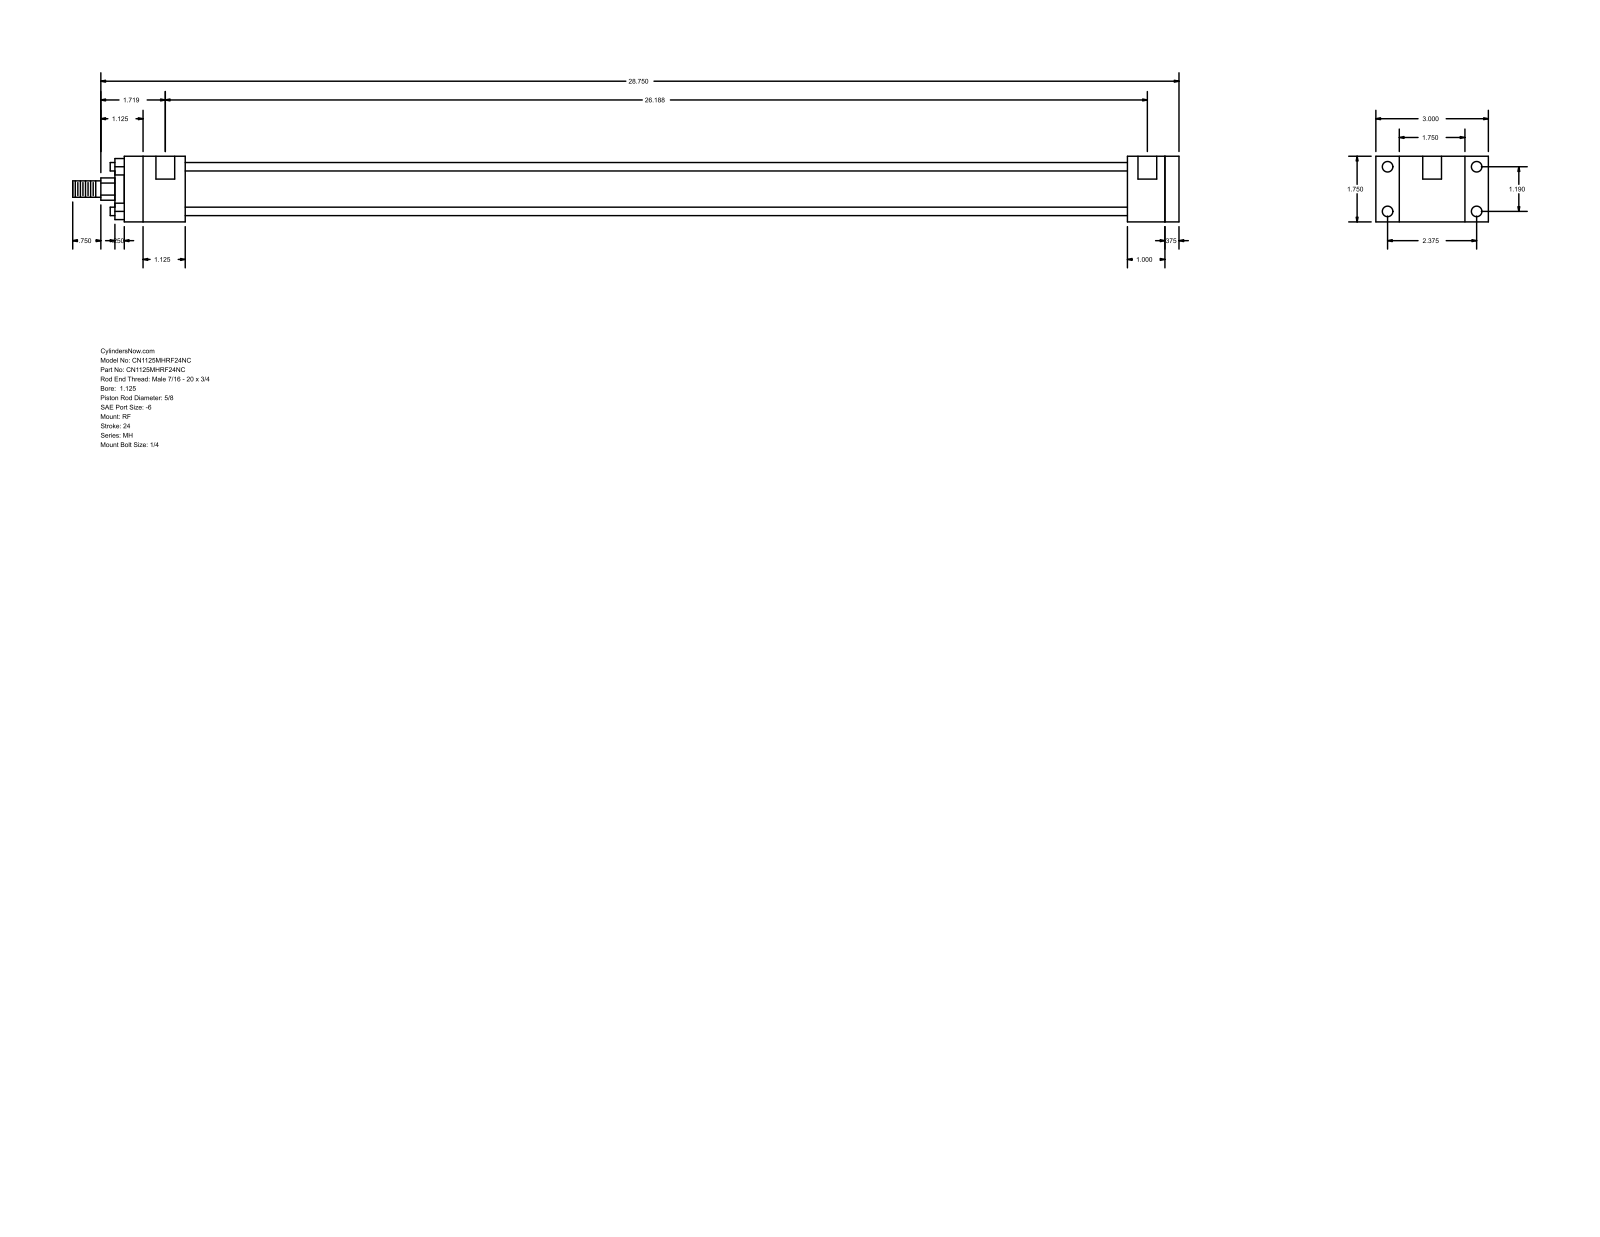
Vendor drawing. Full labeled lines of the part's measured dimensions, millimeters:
Part name (STEP PRODUCT): MH_RF__0112_0.625
STEP written by: GSSL Pune (CONFIG_CONTROL_DESIGN)
Units: millimetres
Bodies: 0 solids, 92 faces (64 planar, 28 cylindrical, 0 other)
Overall size (bounding box): 749.3 × 76.2 × 44.45
Round holes (diameter × count): ⌀5.56 ×4, ⌀7.14 ×4, ⌀12.7 ×2
Round bosses / shafts (diameter × count): ⌀5.71 ×4, ⌀34.92 ×1, ⌀28.57 ×1, ⌀15.88 ×1, ⌀11.11 ×1
Partial cylindrical surfaces — rounded edges, fillets, slot ends (radius × count): R7.54 ×1
Main face-to-face distances: 44.46, 9.52, 25.4, 15.87, 663.58, 673.1, 638.18, 34.92, 41.27, 679.45
Hole centre spacings: 30.22, 60.32, 67.47, 661.99, 3.17, 665.16
